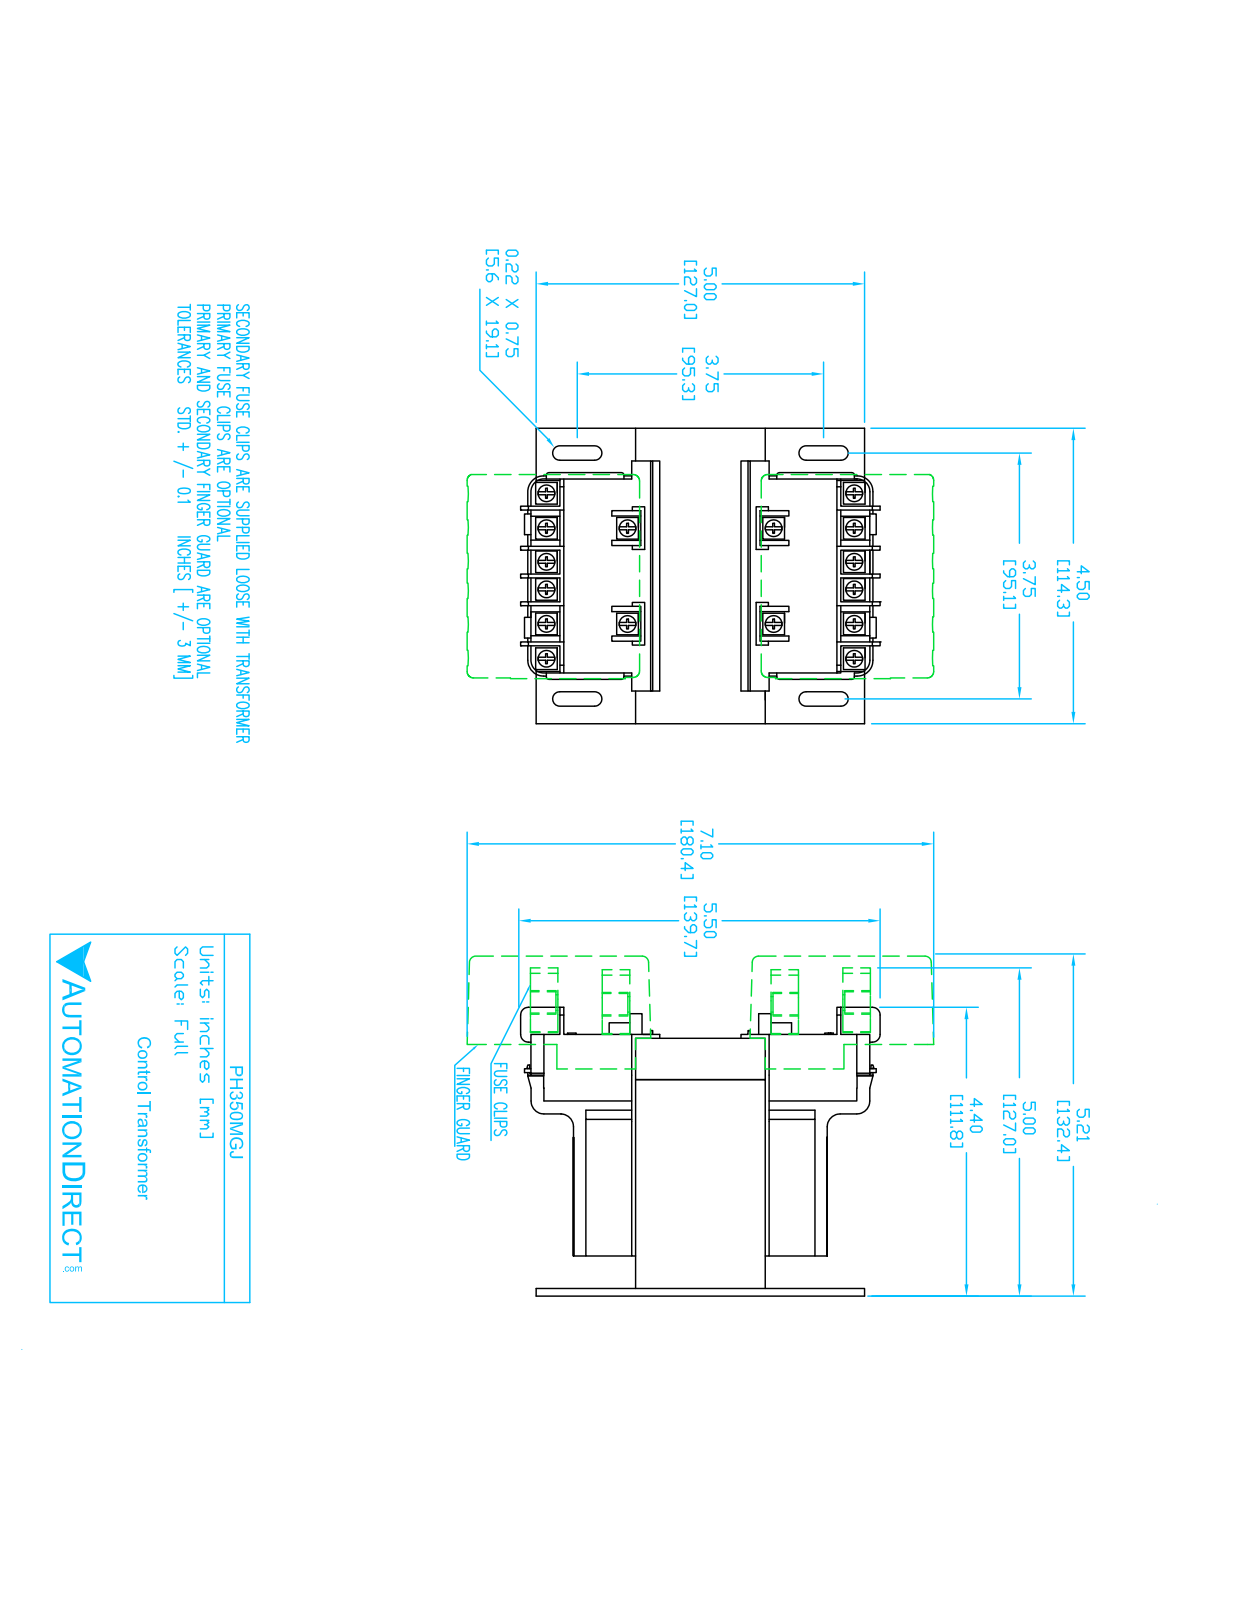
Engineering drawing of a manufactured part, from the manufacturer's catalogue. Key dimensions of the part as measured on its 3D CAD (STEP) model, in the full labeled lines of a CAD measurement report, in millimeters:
Part name (STEP PRODUCT): PH350MGJ
STEP written by: SolidWorks 2017 (AUTOMOTIVE_DESIGN)
Units: millimetres
Bodies: 8 solids, 634 faces (362 planar, 192 cylindrical, 80 other)
Overall size (bounding box): 138.9 × 114.3 × 110
Volume: 1 128 000 mm³ · Surface area: 145 200 mm²
Round holes (diameter × count): ⌀4 ×8
Partial cylindrical surfaces — rounded edges, fillets, slot ends (radius × count): R1 ×90, R5 ×18, R2.8 ×8, R2.5 ×4, R6.2 ×4
Main face-to-face distances: 50, 98, 4.7, 76, 80.7, 16, 107, 31, 26.2, 12
Hole centre spacings: 95.3, 101.4, 9.7, 34.7, 95.7, 25, 98.5, 105.1
